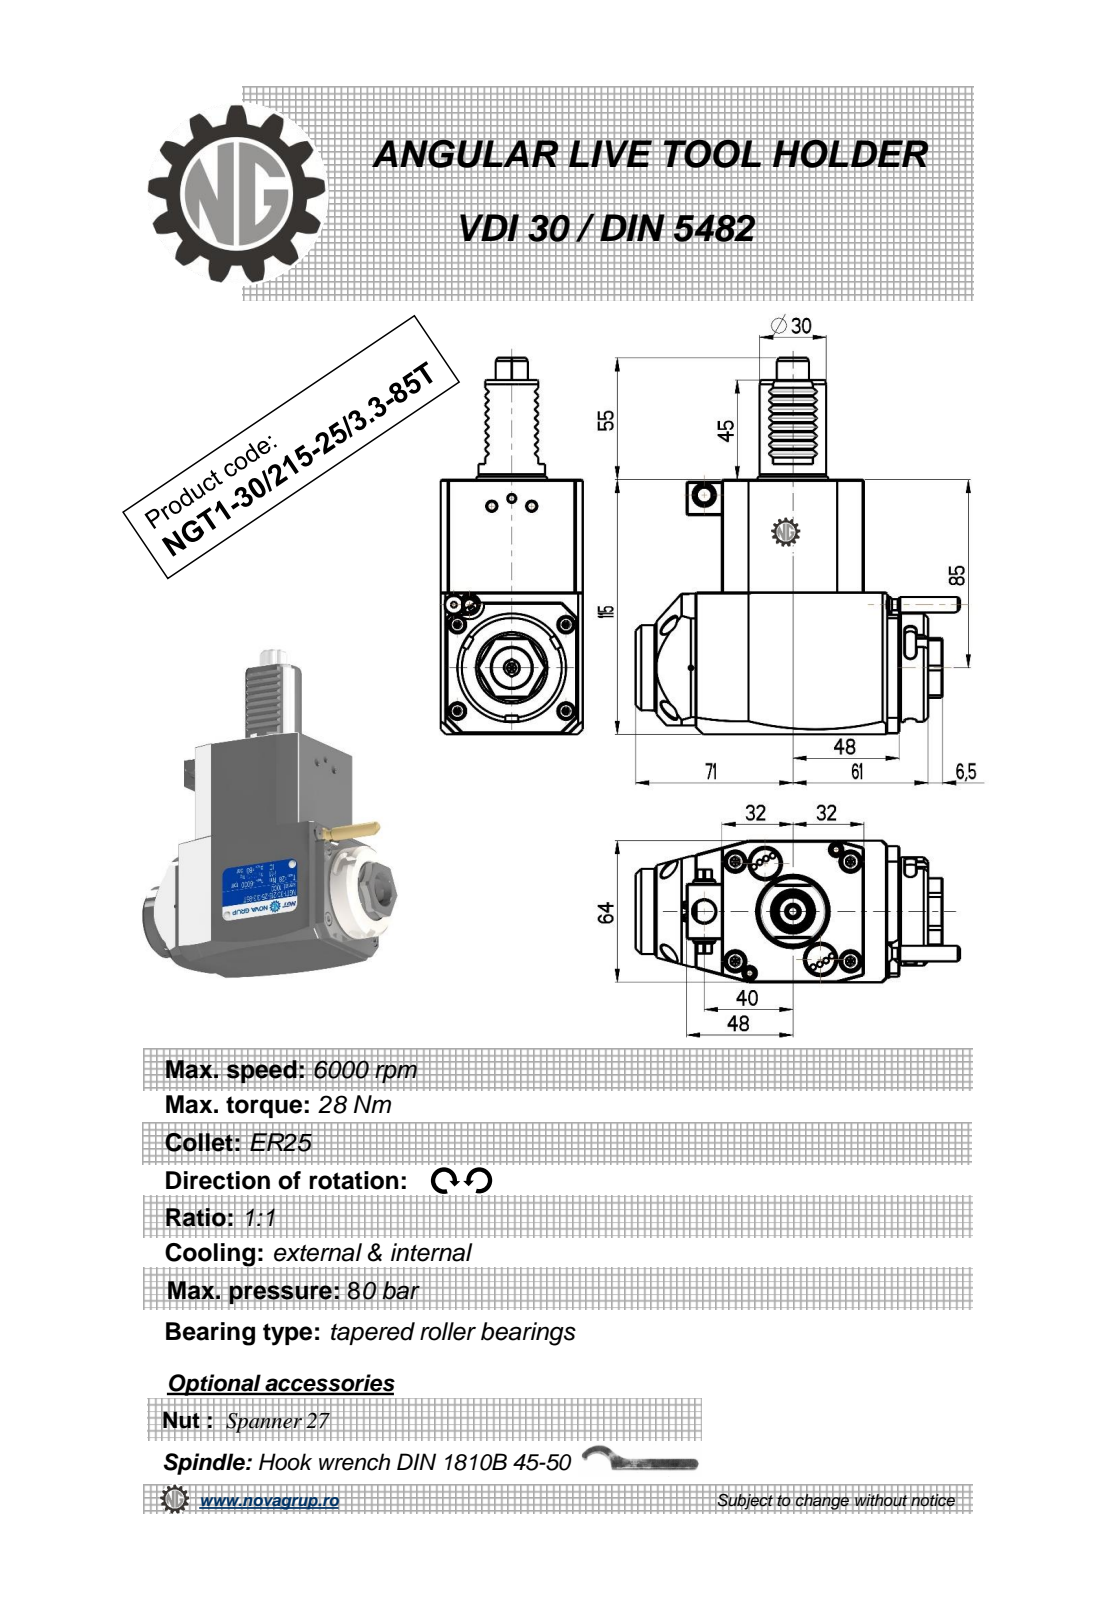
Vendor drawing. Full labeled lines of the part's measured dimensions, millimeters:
Part name (STEP PRODUCT): NGT1_30_215_25_3_3_85T
STEP written by: PRO/ENGINEER BY PARAMETRIC TECHNOLOGY CORPORATION, 2010280 (CONFIG_CONTROL_DESIGN)
Units: millimetres
Bodies: 1 solid, 419 faces (205 planar, 122 cylindrical, 92 other)
Overall size (bounding box): 170 × 146.38 × 64
Volume: 677 324 mm³ · Surface area: 57 531 mm²
Round holes (diameter × count): ⌀2.5 ×1, ⌀3 ×1, ⌀4.2 ×1, ⌀5.3 ×1, ⌀8.5 ×1, ⌀9.5 ×1, ⌀10 ×1, ⌀18 ×1
Round bosses / shafts (diameter × count): ⌀8 ×2, ⌀49 ×1, ⌀42 ×1, ⌀38.5 ×1, ⌀30 ×1, ⌀10 ×1, ⌀7 ×1, ⌀5 ×1
Partial cylindrical surfaces — rounded edges, fillets, slot ends (radius × count): R0.3 ×16, R2.91 ×16, R2.5 ×6, R180 ×2, R3.85 ×1, R4.5 ×1, R5.7 ×1, R7.25 ×1
Main face-to-face distances: 64, 115, 16, 80, 13, 51, 72.18, 29, 93, 2.83
Hole centre spacings: 34.25, 40, 51.62, 76.5
